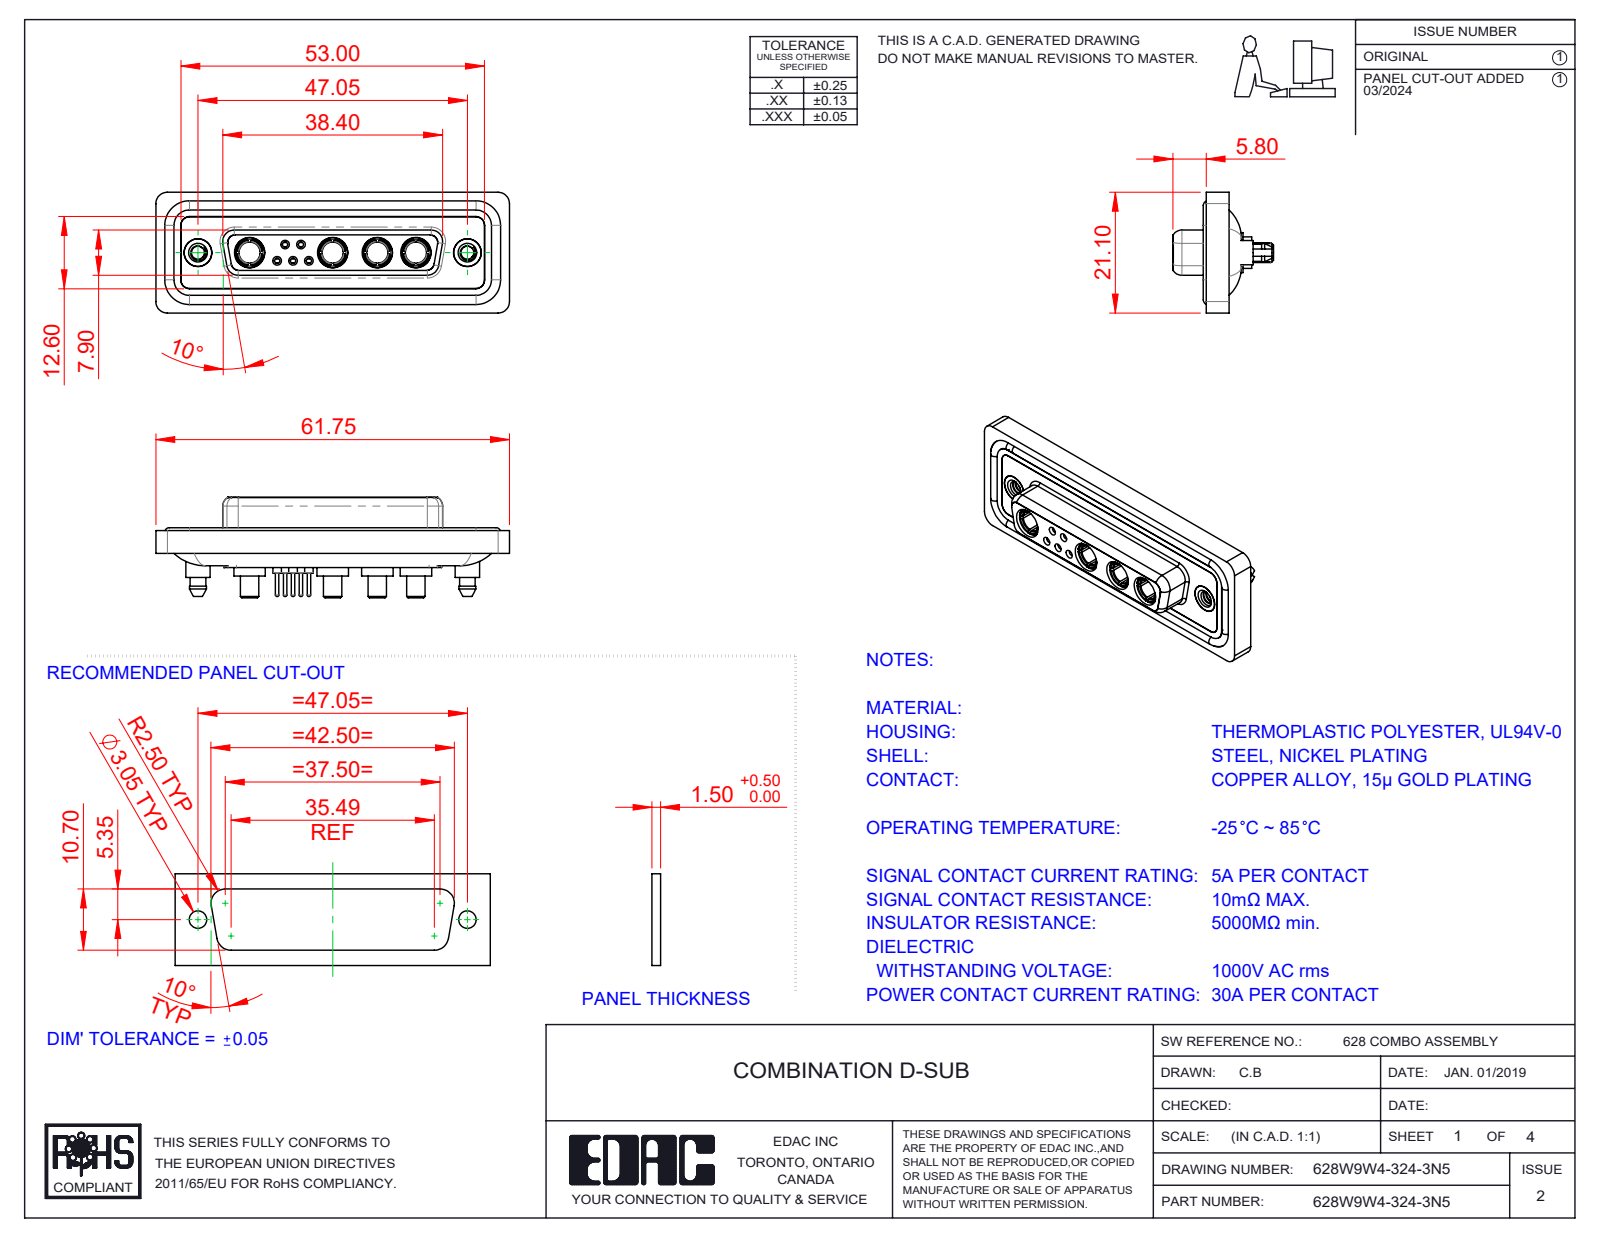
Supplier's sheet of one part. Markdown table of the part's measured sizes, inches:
| quantity | value |
| --- | --- |
| part name | 628Combo Threaded Boardlock_5; 628Combo Shell Rear_25 Contacts; 628Combo Housing_9W4; 628Combo Waterproof Housing_25 Contacts (+5 more) |
| STEP written by | SolidWorks 2023 (CONFIG_CONTROL_DESIGN) |
| units | inches |
| bodies | 20 solids, 1007 faces (312 planar, 407 cylindrical, 288 other) |
| overall size | 2.431 × 0.831 × 0.691 |
| volume | 0.512 in³ |
| surface area | 21.57 in² |
| round holes (diameter × count) | 0.191 × 6, 0.035 × 5, 0.043 × 5, 0.059 × 5, 0.079 × 5, 0.146 × 4, 0.209 × 4, 0.063 × 3, 0.067 × 2, 0.089 × 2, 0.157 × 2, 0.159 × 2 |
| round bosses / shafts (diameter × count) | 0.063 × 6, 0.087 × 5, 0.024 × 5, 0.217 × 4, 0.205 × 4, 0.195 × 4, 0.187 × 4, 0.148 × 4 |
| partial cylindrical surfaces (radius × count) | 0.059 × 24, 0.079 × 18, 0.063 × 10, 0.053 × 8, 0.01 × 4, 0.02 × 4, 0.024 × 4, 0.026 × 4 |
| main face-to-face distances | 0.016, 0.071, 0.293, 0.222, 0.02, 0.278, 0.26, 0.063, 0.043, 0.114 |
| hole center spacings | 0.124, 0.109, 0.198, 0.109, 0.173, 0.198, 0.218, 0.226 |
